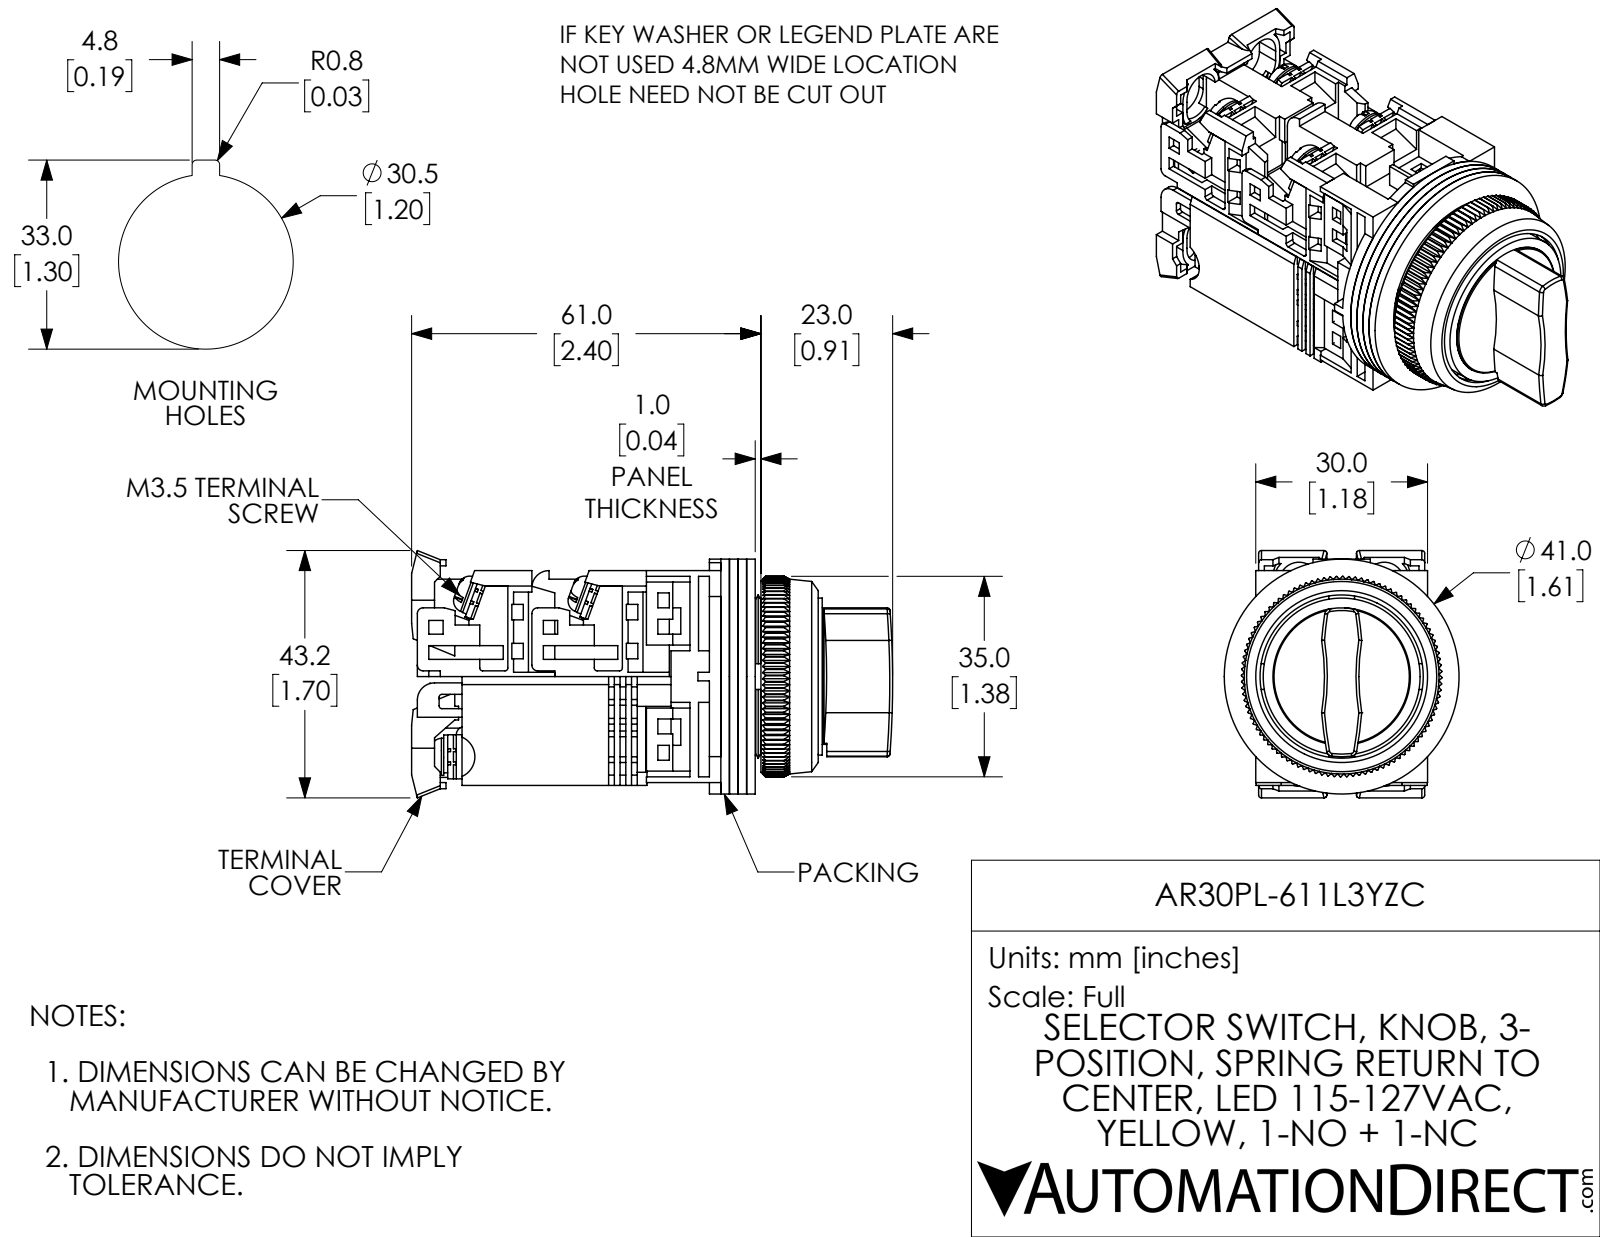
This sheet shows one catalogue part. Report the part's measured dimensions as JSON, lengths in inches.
{"part_name": "AR30PL-611L3YZC", "step_written_by": "SolidWorks 2017 (AUTOMOTIVE_DESIGN)", "units": "inches", "bodies": {"solids": 34, "faces": 2724, "planar": 2033, "cylindrical": 354, "other": 337}, "overall_size": [3.307, 1.7, 1.614], "volume_in3": 3.442, "surface_area_in2": 70.72, "round_holes": [[0.138, 8], [0.142, 6], [0.118, 3], [0.472, 1], [0.709, 1], [0.768, 1], [0.827, 1], [1.122, 1], [1.181, 1], [1.252, 1]], "round_bosses_or_shafts": [[0.26, 6], [0.138, 4], [0.063, 2], [1.614, 1], [1.15, 1], [1.079, 1], [0.945, 1], [0.886, 1]], "partial_cylinders_radius": [[0.059, 25], [0.02, 15], [0.039, 8], [0.138, 4], [0.177, 4], [0.118, 3], [1.575, 2], [2.953, 2]], "face_to_face_distances": [0.059, 0.118, 0.177, 0.039, 0.748, 0.079, 0.787, 0.063, 0.689, 0.197], "hole_center_spacings": [0.579, 0.269, 0.638, 0.297, 0.624, 0.02, 0.302, 0.583]}
